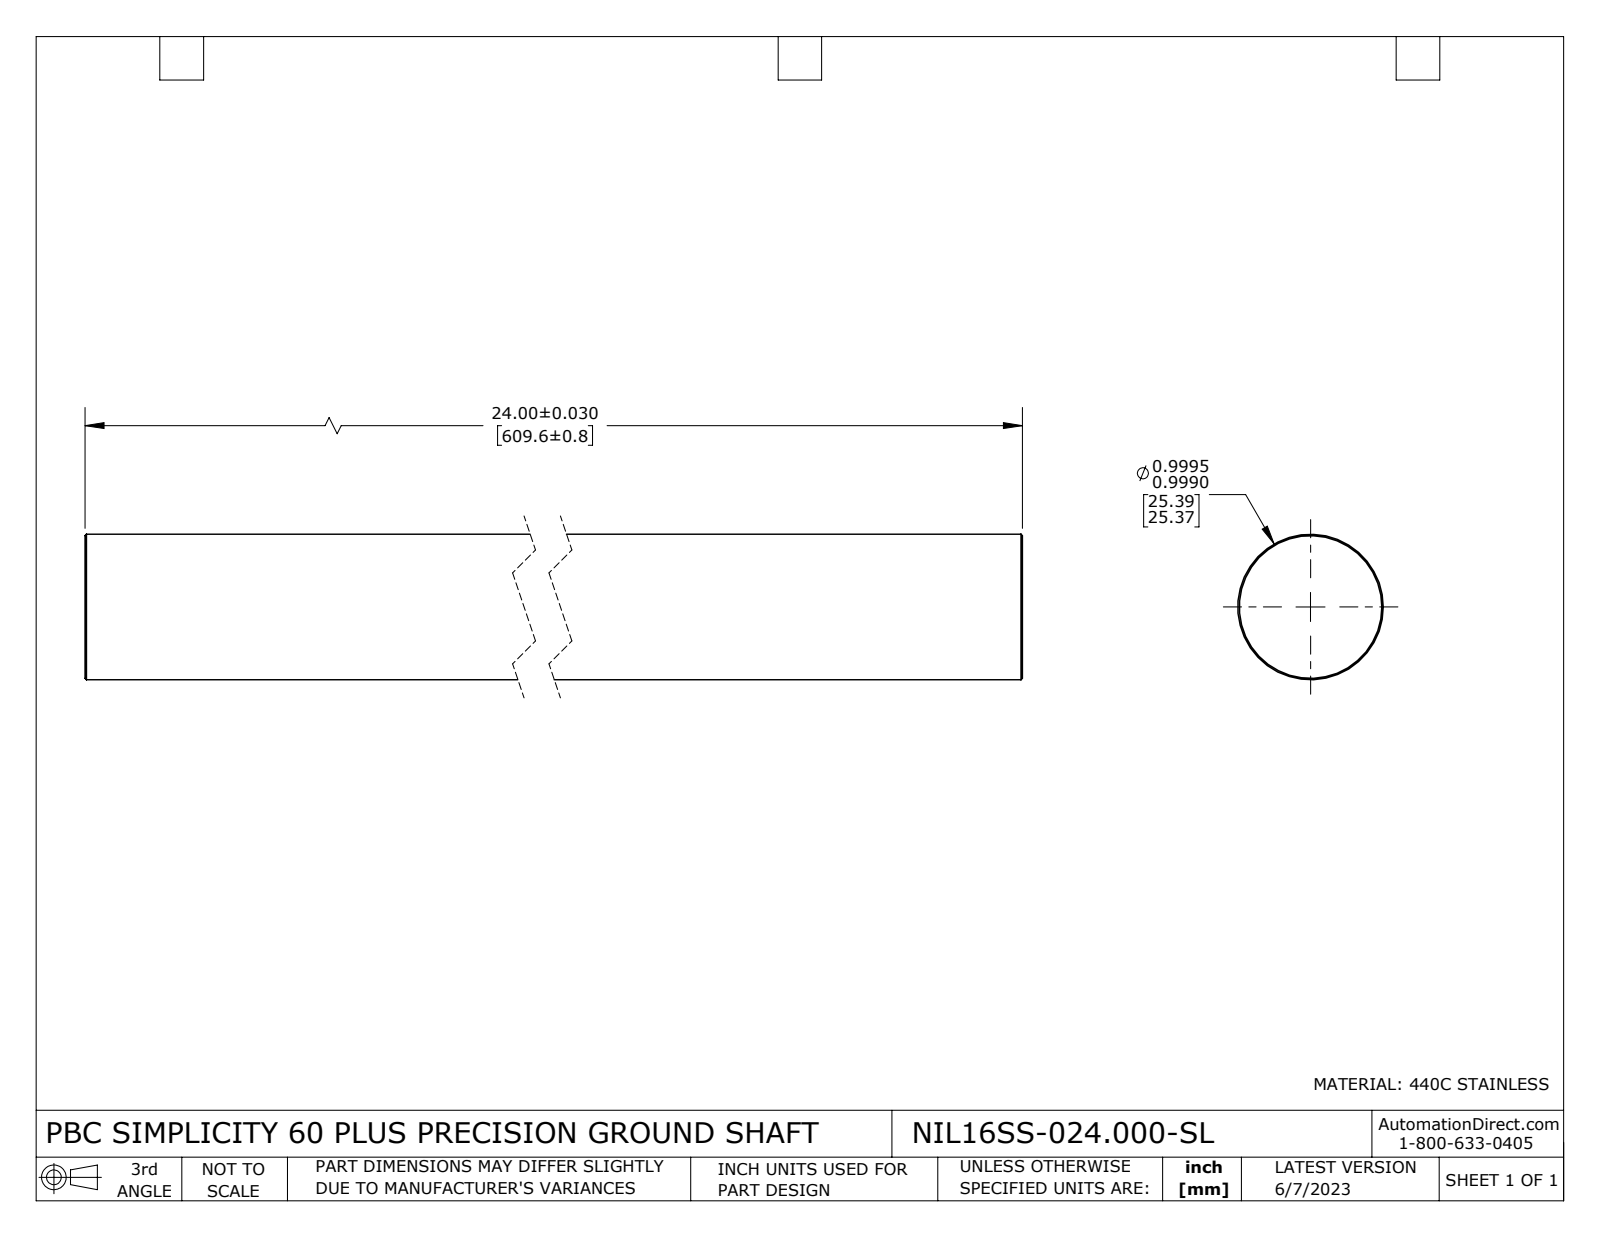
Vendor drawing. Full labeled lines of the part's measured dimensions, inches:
Part name (STEP PRODUCT): NIL16SS-024.000-SL
STEP written by: SolidWorks 2021 (CONFIG_CONTROL_DESIGN)
Units: inches
Bodies: 1 solid, 8 faces (2 planar, 2 cylindrical, 4 other)
Overall size (bounding box): 24 × 1 × 1
Volume: 18.85 in³ · Surface area: 76.93 in²
Round bosses / shafts (diameter × count): ⌀1 ×1
Main face-to-face distances: 24
